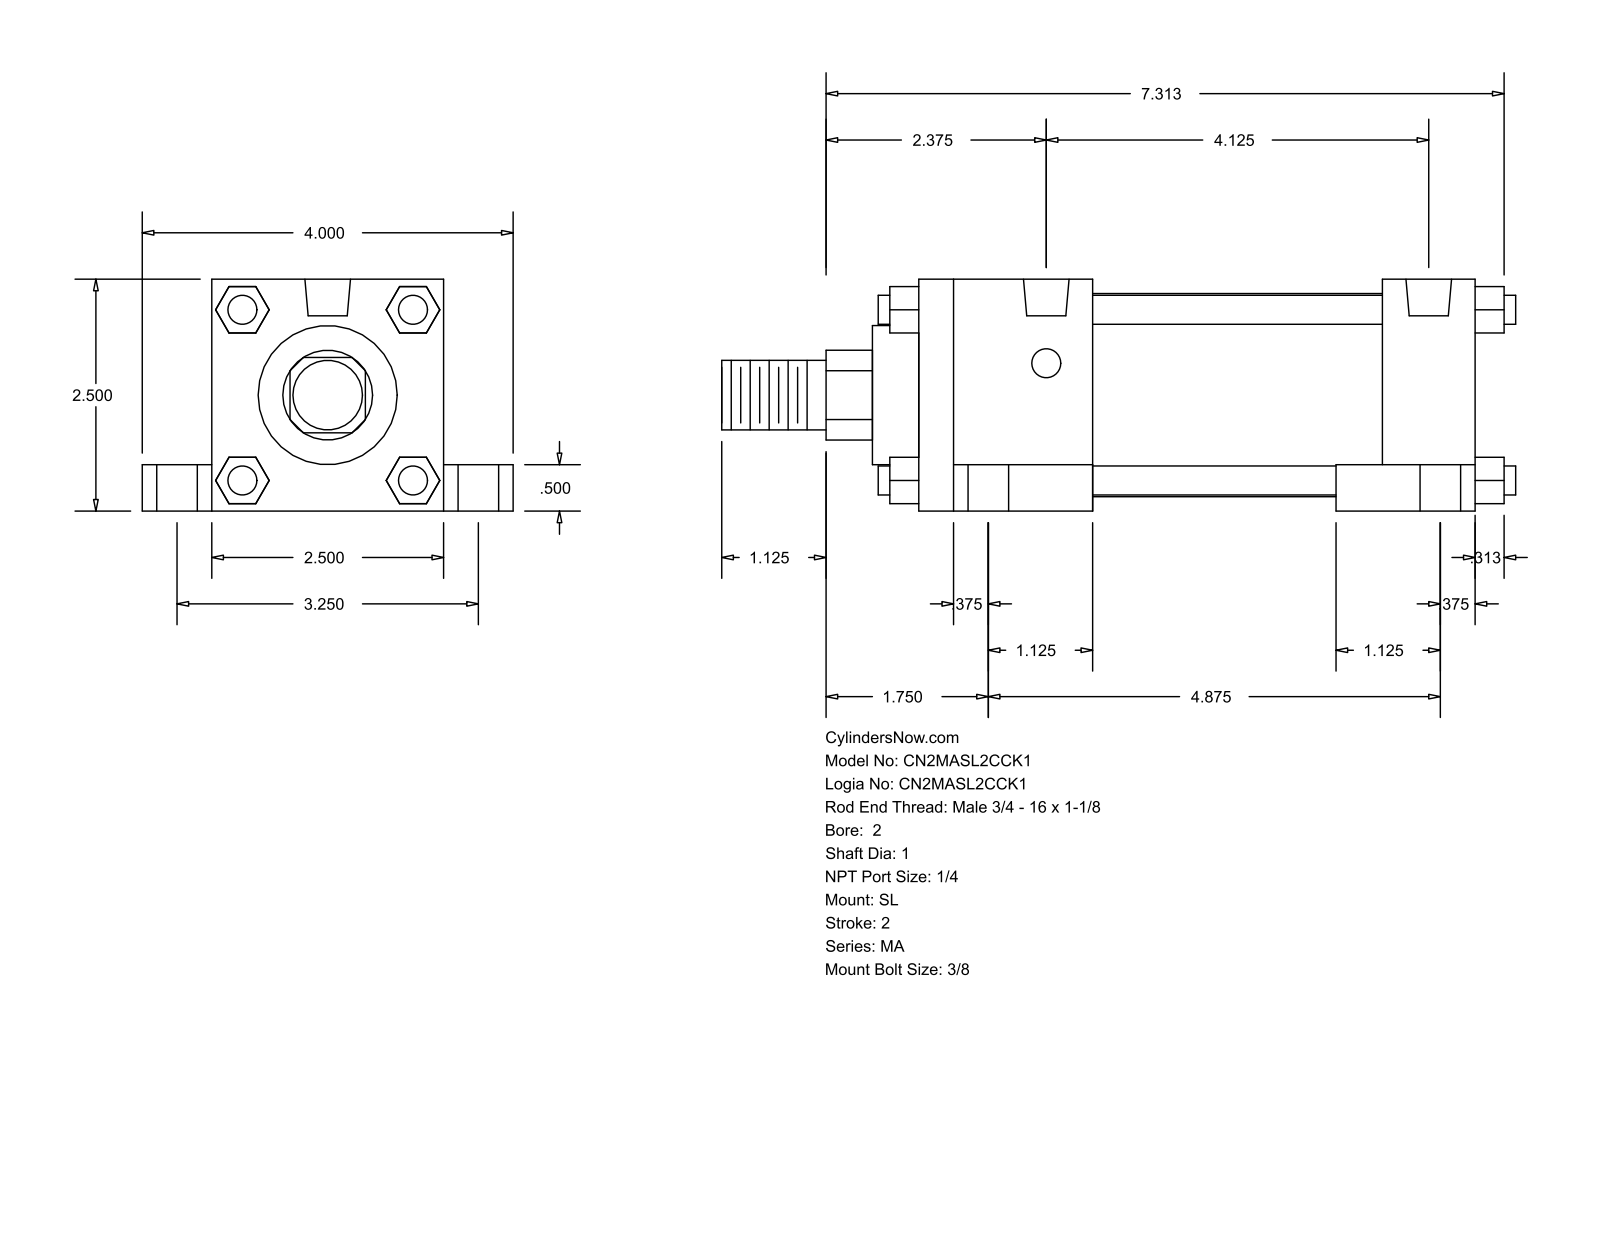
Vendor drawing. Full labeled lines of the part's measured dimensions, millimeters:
Part name (STEP PRODUCT): MA_SL__0200_1
STEP written by: GSSL Pune (CONFIG_CONTROL_DESIGN)
Units: millimetres
Bodies: 0 solids, 148 faces (112 planar, 36 cylindrical, 0 other)
Overall size (bounding box): 217.49 × 101.6 × 63.5
Round holes (diameter × count): ⌀7.94 ×4, ⌀11.11 ×4, ⌀17.46 ×4, ⌀12.49 ×2
Round bosses / shafts (diameter × count): ⌀7.94 ×4, ⌀55.63 ×1, ⌀38.1 ×1, ⌀25.4 ×1, ⌀19.05 ×1
Partial cylindrical surfaces — rounded edges, fillets, slot ends (radius × count): R12.29 ×1
Main face-to-face distances: 63.5, 12.7, 152.4, 19.05, 82.55, 25.4, 50.8, 47.63, 104.77, 127
Hole centre spacings: 41.39, 44.22, 82.54, 104.77, 115.57, 123.83, 127.51, 148.82
